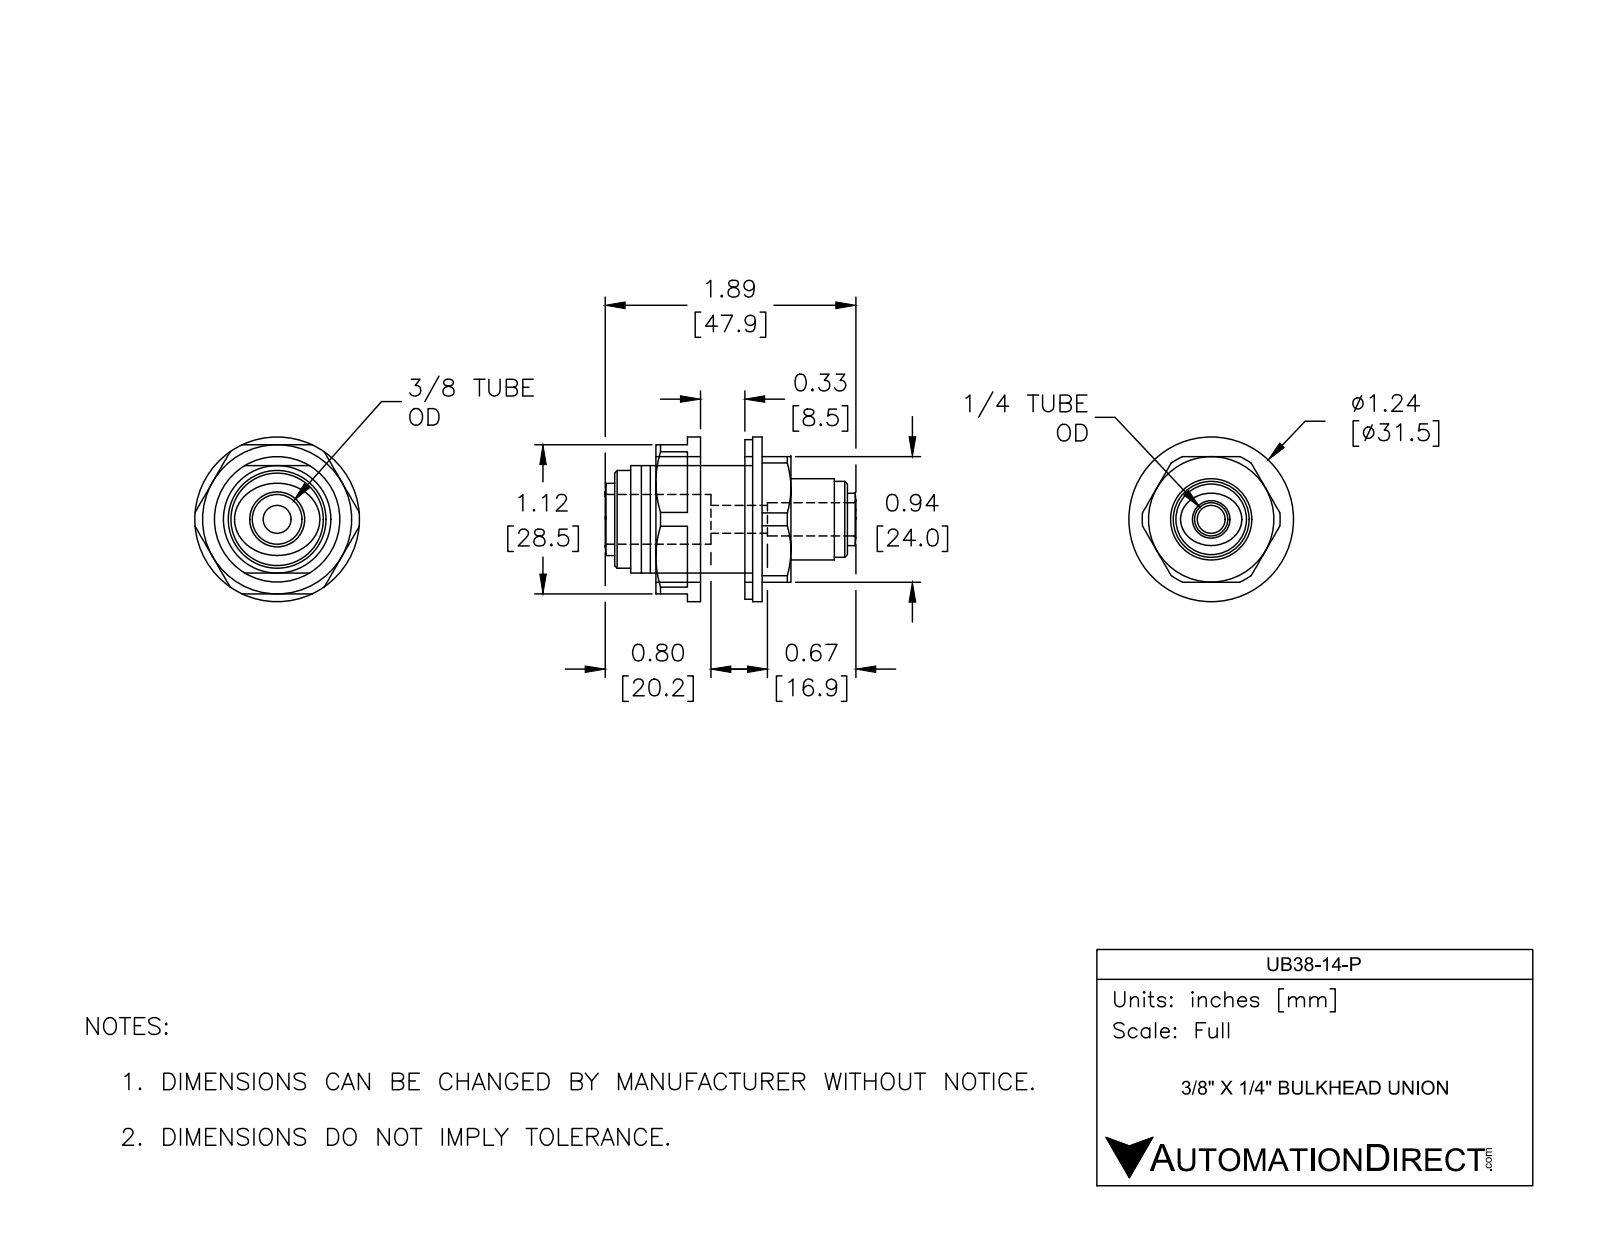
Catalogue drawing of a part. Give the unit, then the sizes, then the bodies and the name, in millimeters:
Units: millimetres
Overall size (bounding box): 47.9 × 31.5 × 31.5
Round holes (diameter × count): ⌀5.3 ×1, ⌀6.4 ×1, ⌀9.5 ×1
Round bosses / shafts (diameter × count): ⌀31.5 ×1, ⌀30.5 ×1, ⌀24 ×1, ⌀20.5 ×1, ⌀18.7 ×1, ⌀15.5 ×1, ⌀14.5 ×1
Partial cylindrical surfaces — rounded edges, fillets, slot ends (radius × count): R13.2 ×1
Main face-to-face distances: 8.5, 2.3, 26.2, 11.8, 3.3, 5.5, 8.8, 17.3, 20.5, 28.5
Volume: 17 450 mm³ · Surface area: 7 039 mm²
Bodies: 1 solid, 102 faces (34 planar, 37 cylindrical, 31 other)
Part name (STEP PRODUCT): UB38-14-P
STEP written by: SolidWorks 2017 (AUTOMOTIVE_DESIGN)
